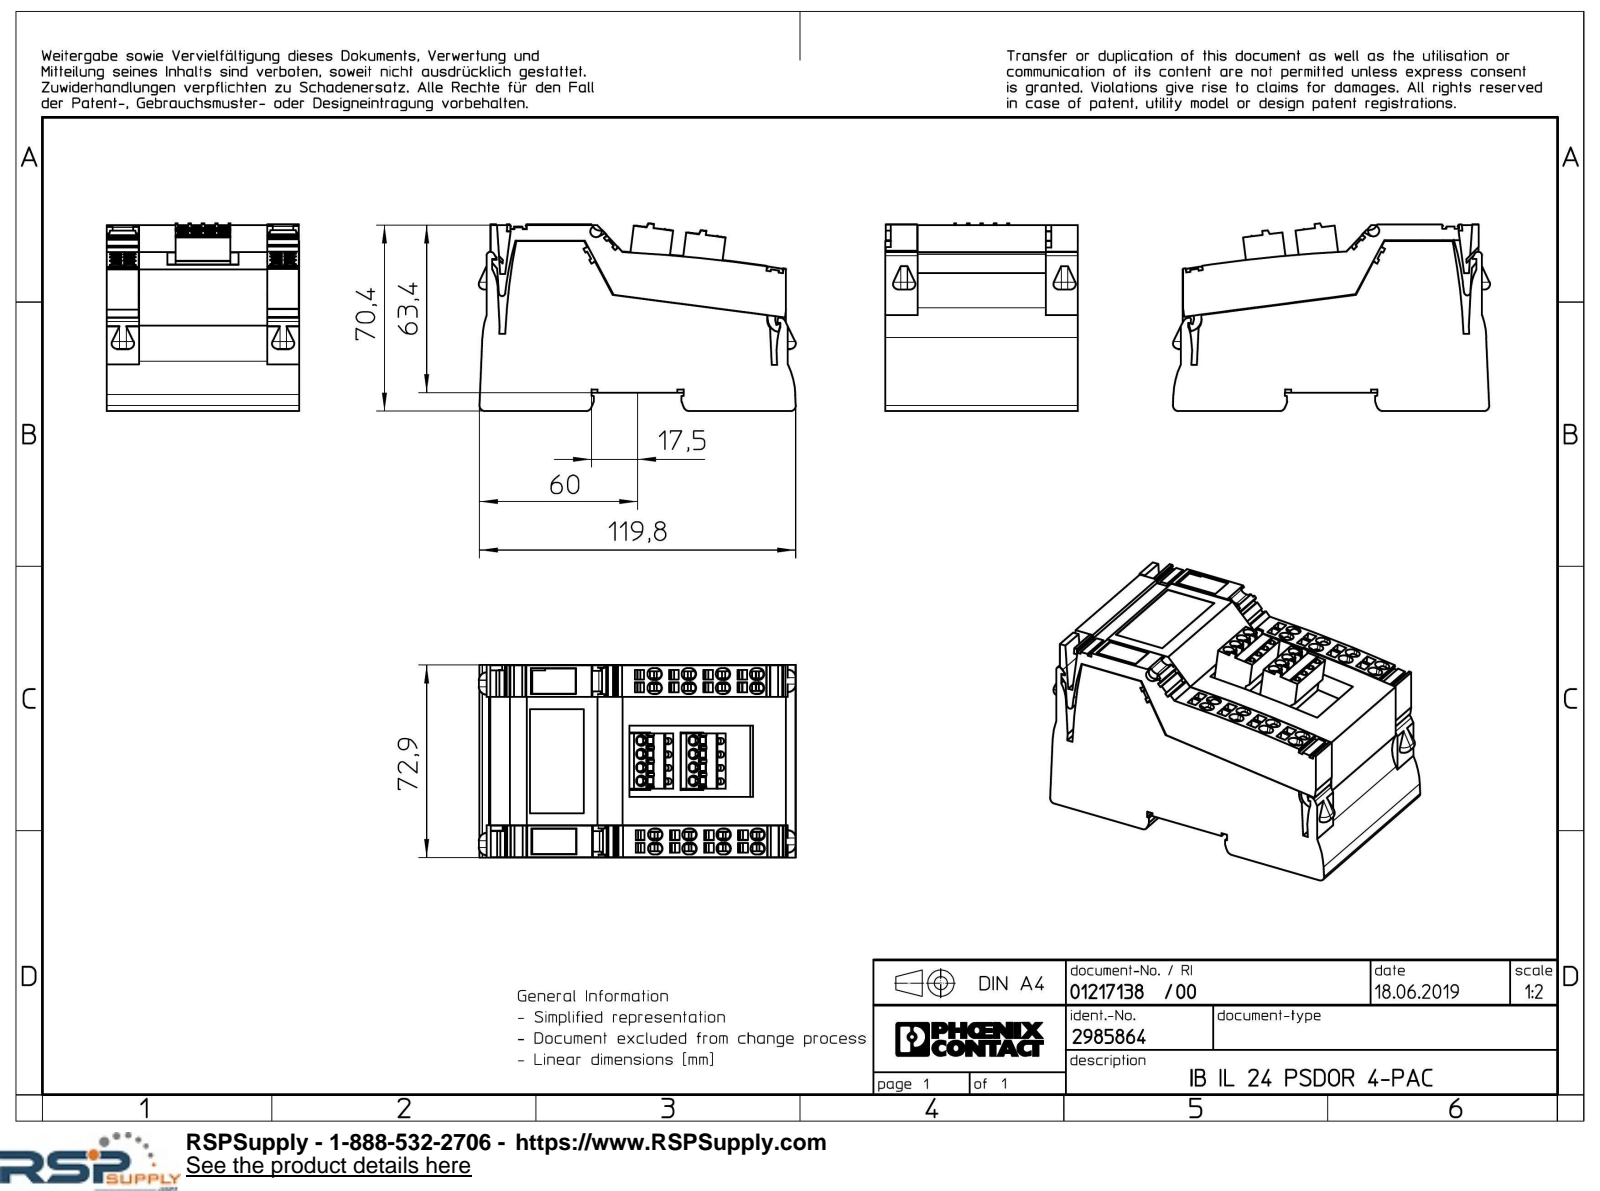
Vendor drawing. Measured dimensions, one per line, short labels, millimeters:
name: IL_24_P_SDOR_4_YE_1018-select; L_L_LWL_RD_3027_AUSSEN-select; L_L_LWL_RD_3027-select; FKCS_2.5_4_ST_5.08_BUGY_7031-select (+2 more)
written by: Creo Elements/Direct Modeling 20.1A 29-Sep-2018 (C) Parametric Technology GmbH (AUTOMOTIVE_DESIGN)
unit: mm
bodies: 7 solids, 1730 faces (1418 planar, 224 cylindrical, 88 other)
size: 120.11 × 72.9 × 71.05
volume: 494 365 mm³; area: 77 444 mm²
holes: 12× ⌀1.2, 8× ⌀1.4, 8× ⌀4, 6× ⌀2.8
bosses: 6× ⌀2.8
rounds: 32× R2.25, 8× R1.18, 8× R1.5, 8× R2.92, 8× R2.98, 6× R2, 4× R0.6, 4× R1.4
face distances: 60.75, 72.9, 12.15, 12.1, 12.05, 12, 7, 48.6, 60.8, 60.7
hole spacings: 5.08, 13, 13.86, 4.8, 5.36, 10.16, 20.64, 20.65
